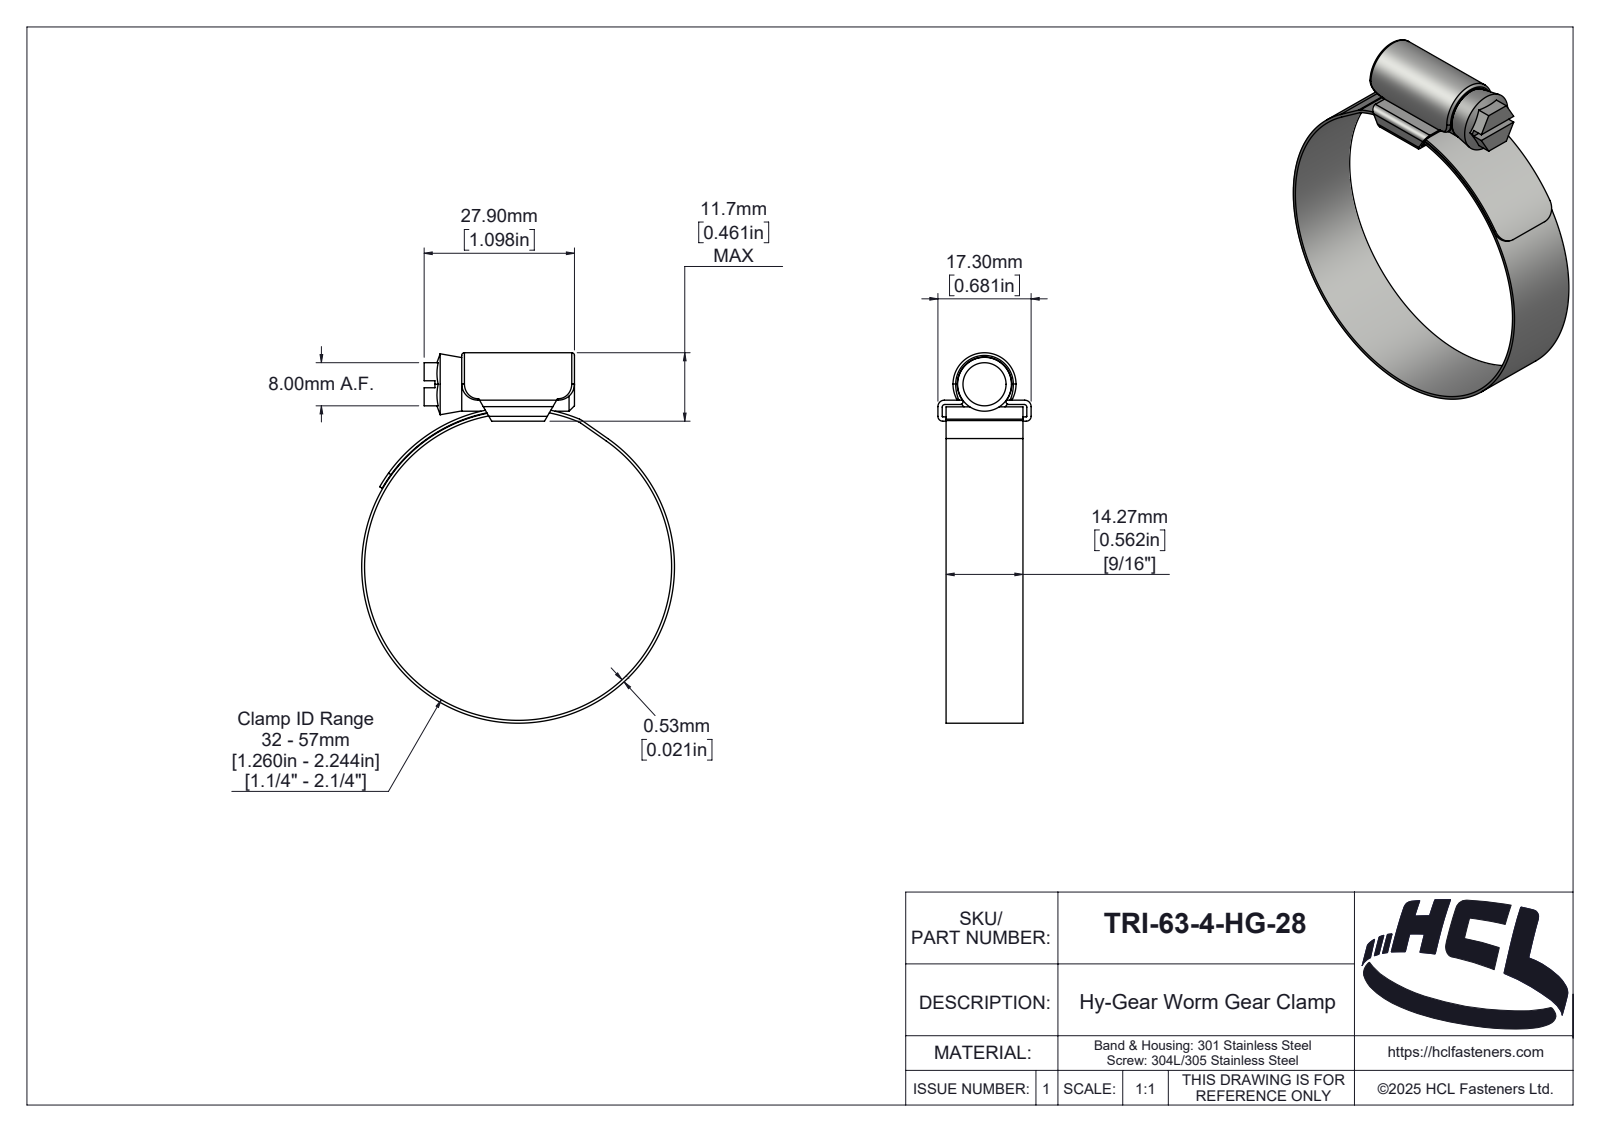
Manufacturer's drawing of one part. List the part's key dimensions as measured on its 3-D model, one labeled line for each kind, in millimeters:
Part name (STEP PRODUCT): TRI-50-0-HG-28
STEP written by: SolidWorks 2025 (AUTOMOTIVE_DESIGN)
Units: millimetres
Bodies: 3 solids, 189 faces (39 planar, 89 cylindrical, 61 other)
Overall size (bounding box): 68.73 × 58.06 × 17.3
Volume: 4 392 mm³ · Surface area: 9 070 mm²
Round holes (diameter × count): ⌀57 ×1
Round bosses / shafts (diameter × count): ⌀58.06 ×1, ⌀10 ×1
Partial cylindrical surfaces — rounded edges, fillets, slot ends (radius × count): R0.5 ×6, R3 ×4, R0.1 ×2, R0.9 ×2, R1.2 ×2, R0.46 ×1, R1.89 ×1, R2 ×1
Main face-to-face distances: 0.8, 3.1, 14.26, 2.3, 0.53, 3.9, 27.9, 1.52, 15.78, 16.5
